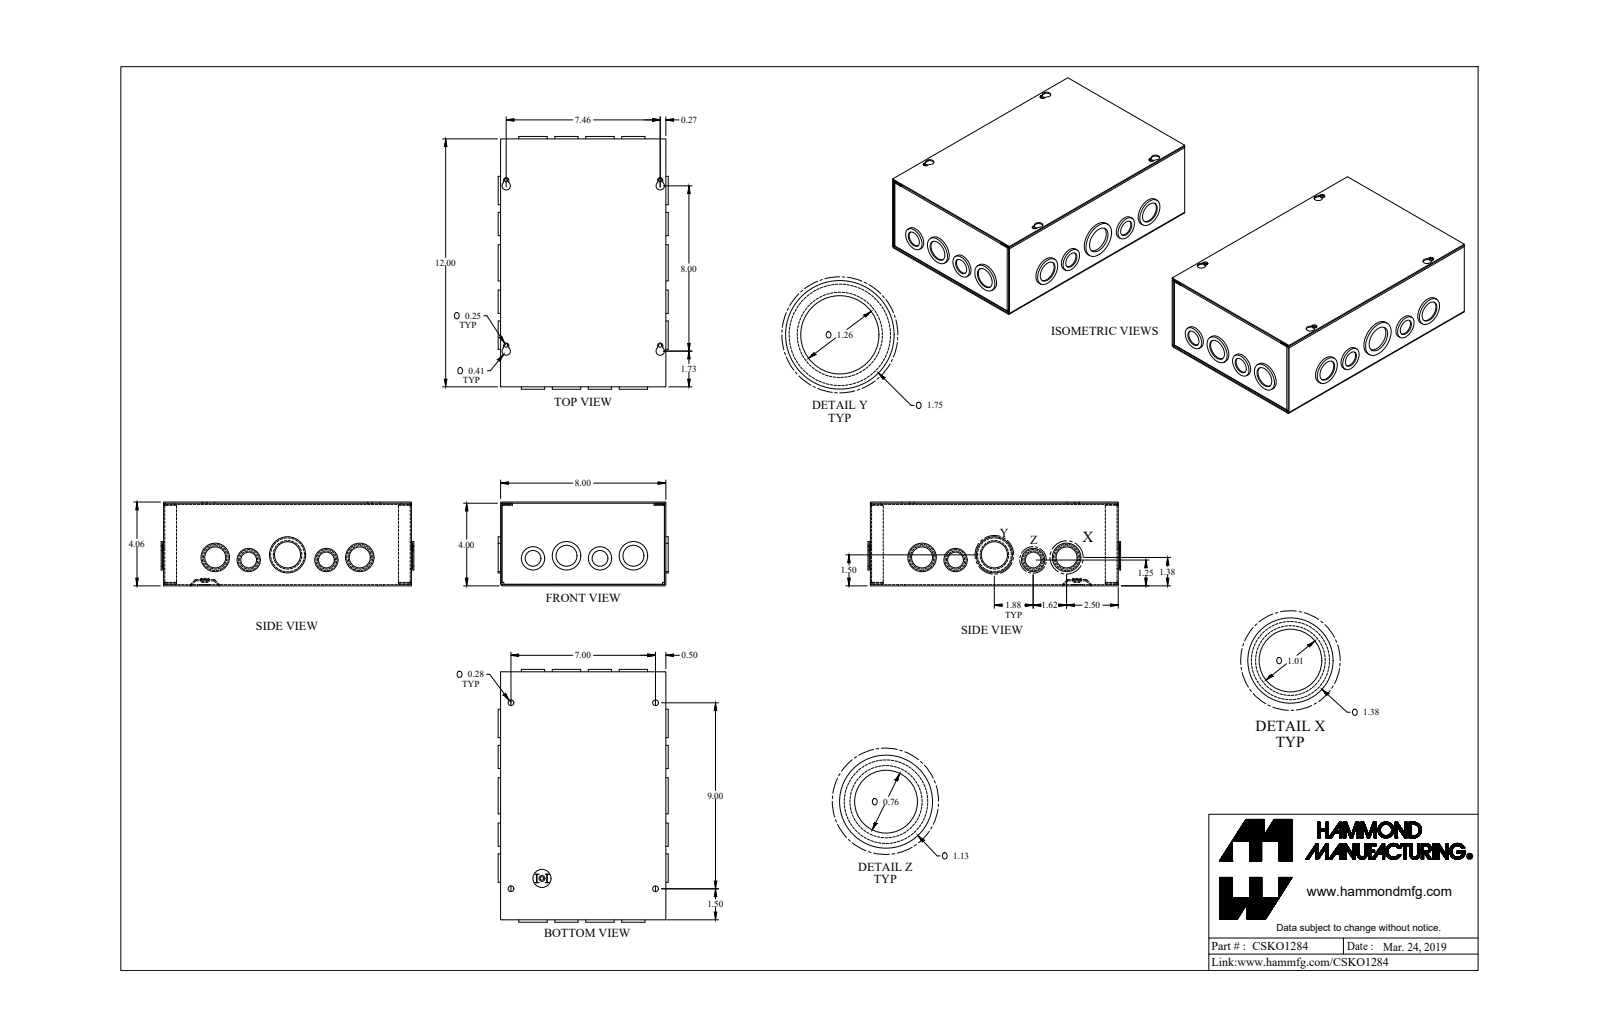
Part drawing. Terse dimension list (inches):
name: CSKO1284_Default
written by: SolidWorks 2019 (CONFIG_CONTROL_DESIGN)
unit: in
bodies: 4 solids, 421 faces (197 planar, 216 cylindrical, 8 other)
size: 12.234 × 8.234 × 4.057
volume: 22.3 in³; area: 791.8 in²
holes: 12× ⌀1.011, 7× ⌀1.261, 6× ⌀0.761, 5× ⌀0.17, 4× ⌀0.281, 1× ⌀0.5, 1× ⌀1.636
bosses: 7× ⌀1.125, 6× ⌀1.375, 6× ⌀0.875, 5× ⌀1.125, 2× ⌀0.875, 1× ⌀1.75, 1× ⌀1.375, 1× ⌀0.492
rounds: 12× R0.029, 12× R0.086, 8× R0.057, 4× R0.125, 4× R0.203
face distances: 0.057, 4, 3.943, 4.057, 7.943, 11.943, 8, 7.886, 12, 0.114
hole spacings: 1.625, 0.125, 0.55, 1.62, 3.24, 3.242, 7.247, 8.503
